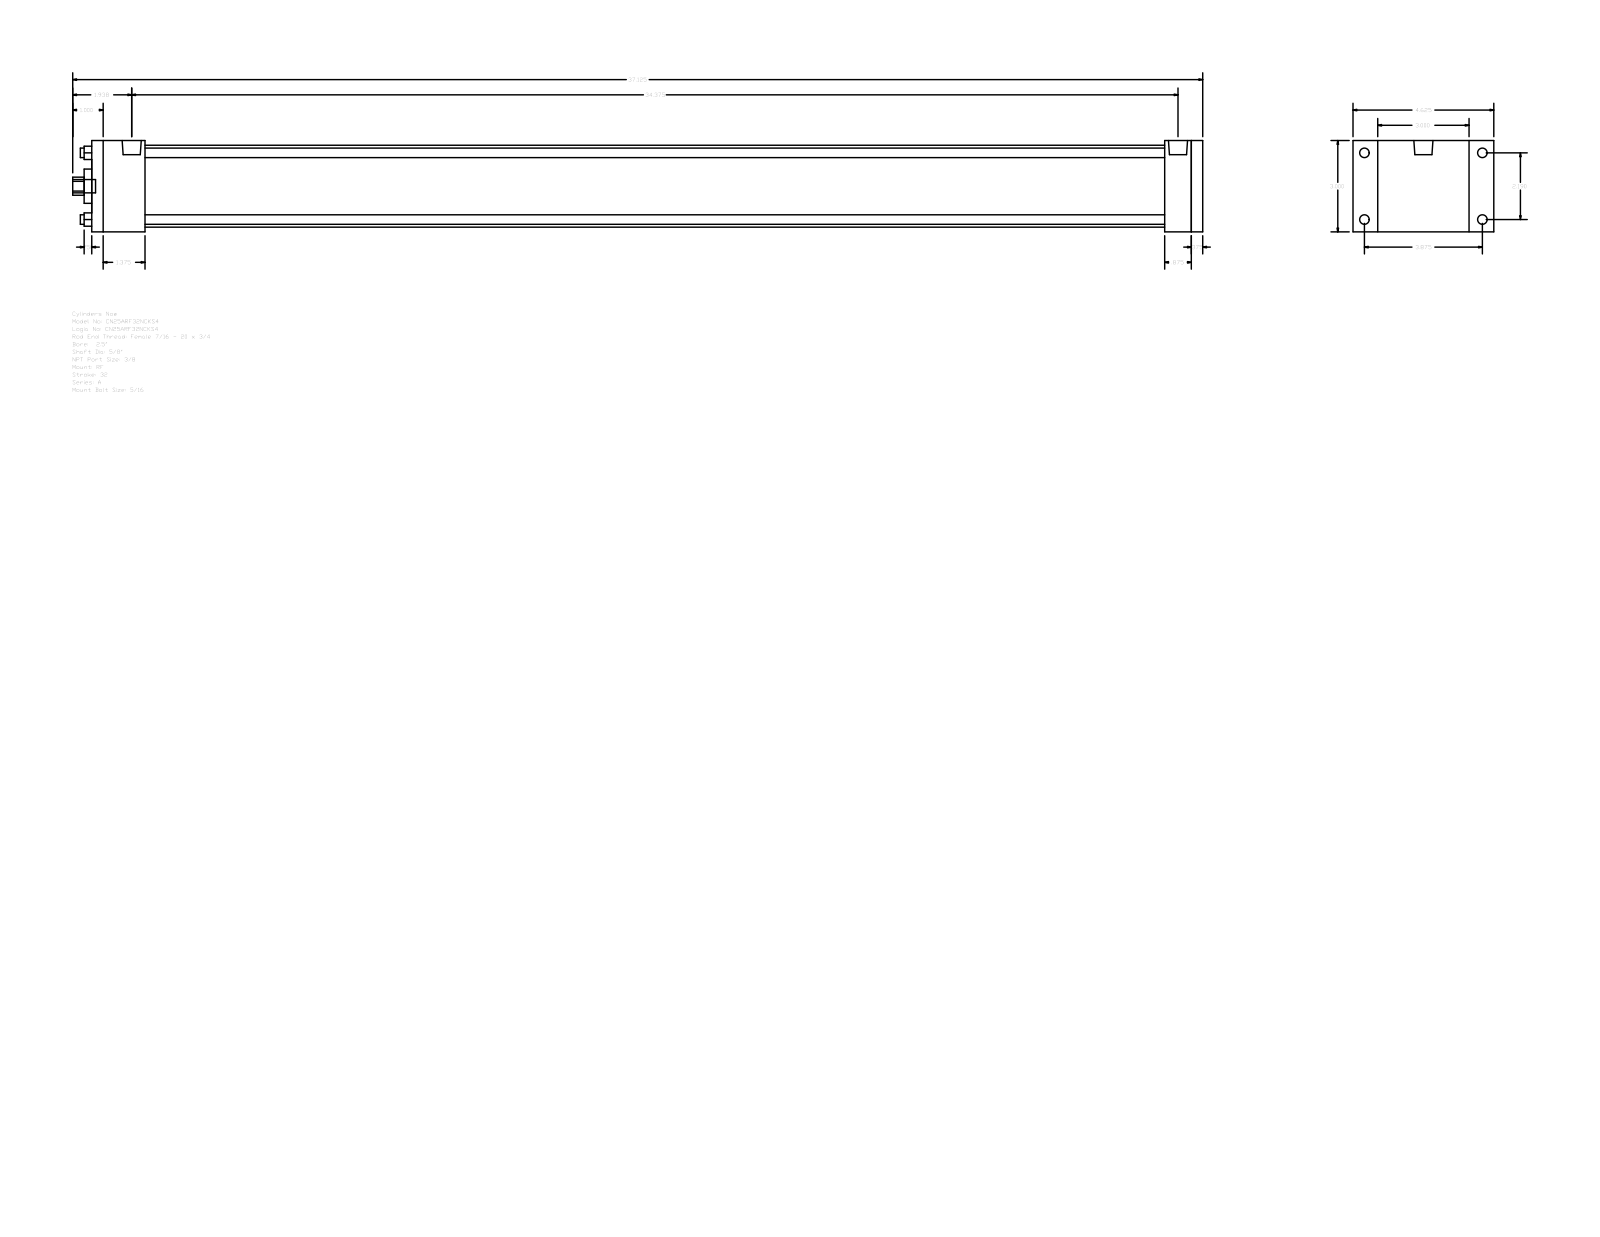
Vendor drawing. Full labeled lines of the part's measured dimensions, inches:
Part name (STEP PRODUCT): A_RF__0250_0.625
STEP written by: GSSL Pune (CONFIG_CONTROL_DESIGN)
Units: inches
Bodies: 0 solids, 92 faces (64 planar, 28 cylindrical, 0 other)
Overall size (bounding box): 37.125 × 4.625 × 3
Round holes (diameter × count): ⌀0.313 ×4, ⌀0.625 ×1, ⌀1.125 ×1, ⌀2.69 ×1
Round bosses / shafts (diameter × count): ⌀0.313 ×4, ⌀0.219 ×4, ⌀0.627 ×2, ⌀0.437 ×1
Partial cylindrical surfaces — rounded edges, fillets, slot ends (radius × count): R0.297 ×1
Main face-to-face distances: 3, 36.5, 0.375, 36.125, 1.75, 1.25, 35.25, 33.5, 34.375, 34.75
Hole centre spacings: 1.548, 2.19, 3.097
